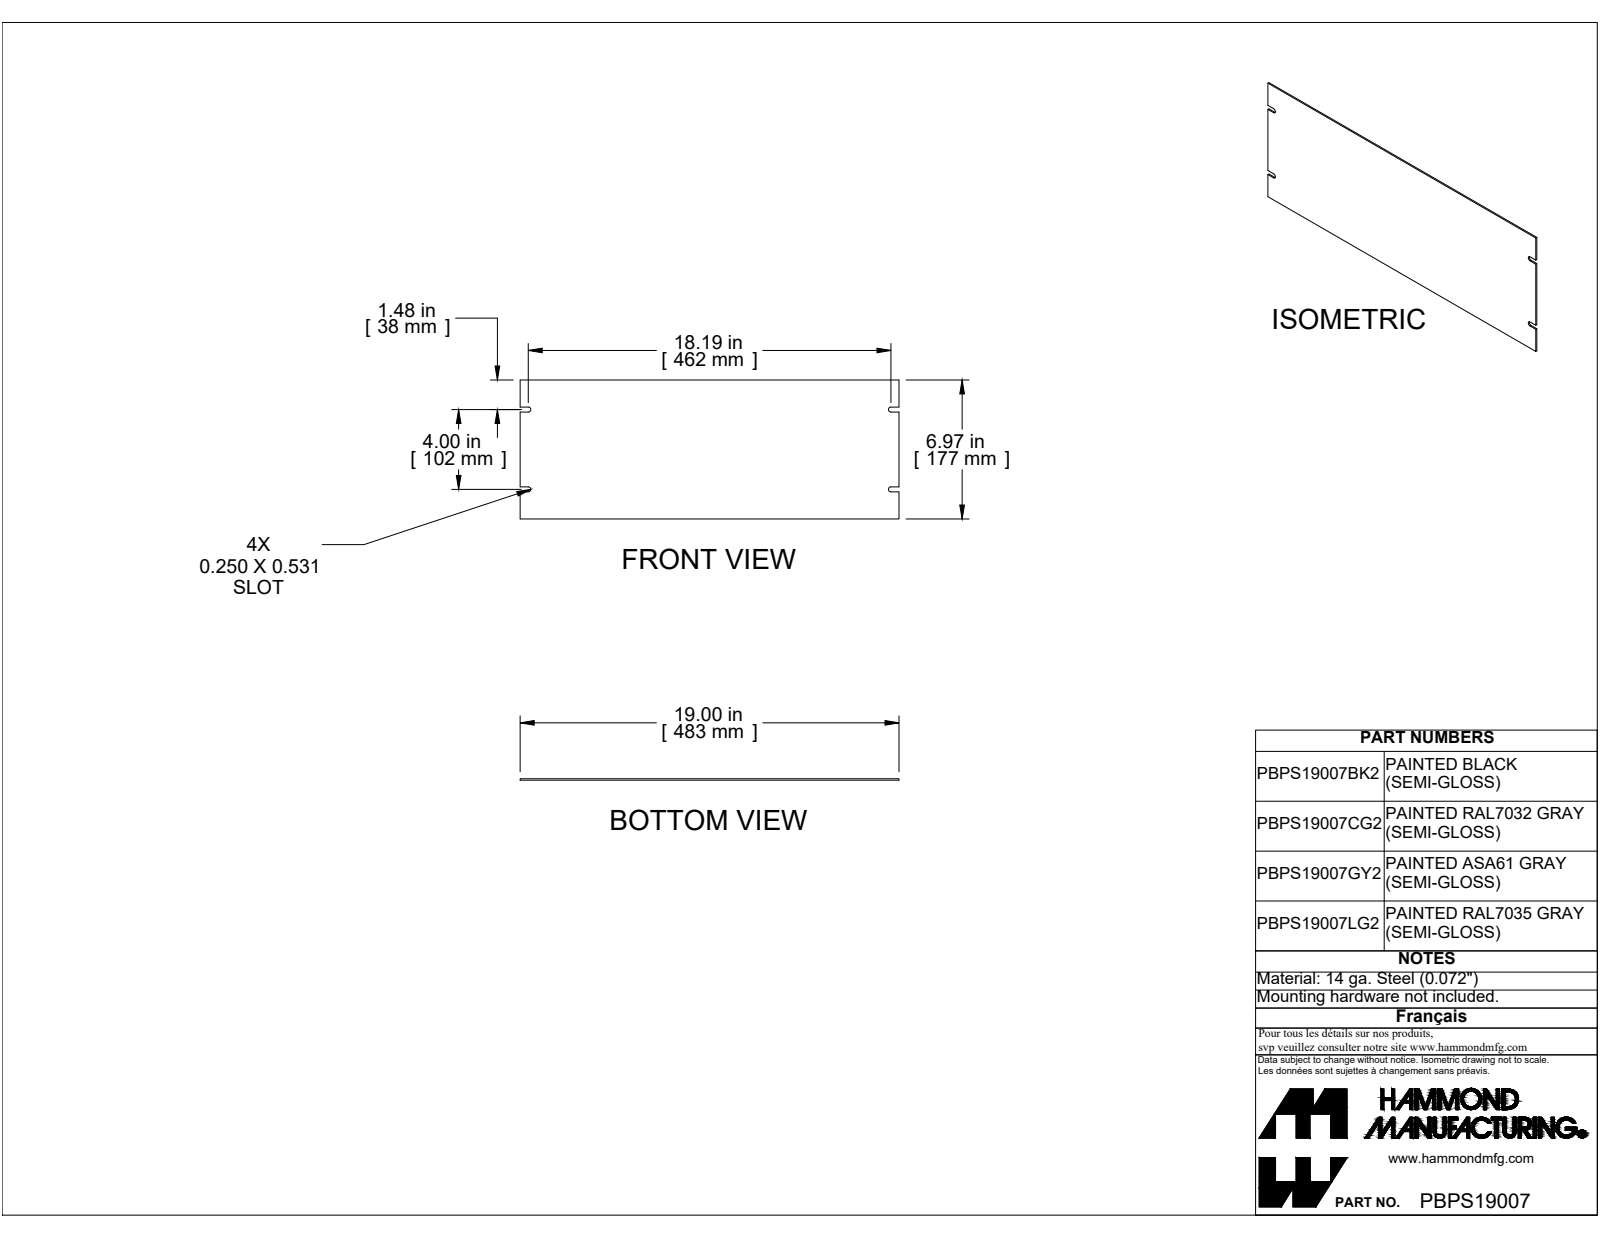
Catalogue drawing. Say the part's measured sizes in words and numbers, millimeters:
The part is named "PBPS19007BK". Its 3-D file was written by "SolidWorks 2019 (CONFIG_CONTROL_DESIGN)". It is 1 solid with 22 faces: 18 planar, 4 cylindrical and 0 other. Overall it measures 482.6 by 177 by 1.8 millimeters. Its volume is 155 600 cubic millimeters and its surface area 172 800 square millimeters. Partial cylindrical surfaces (rounded edges, fillets, slot ends): 4 of radius 3.2. The main face-to-face distances are 1.8, 177, 482.6, 34.5, 142.5, 40.9, 136.1, 6.4, 101.6, 108.
